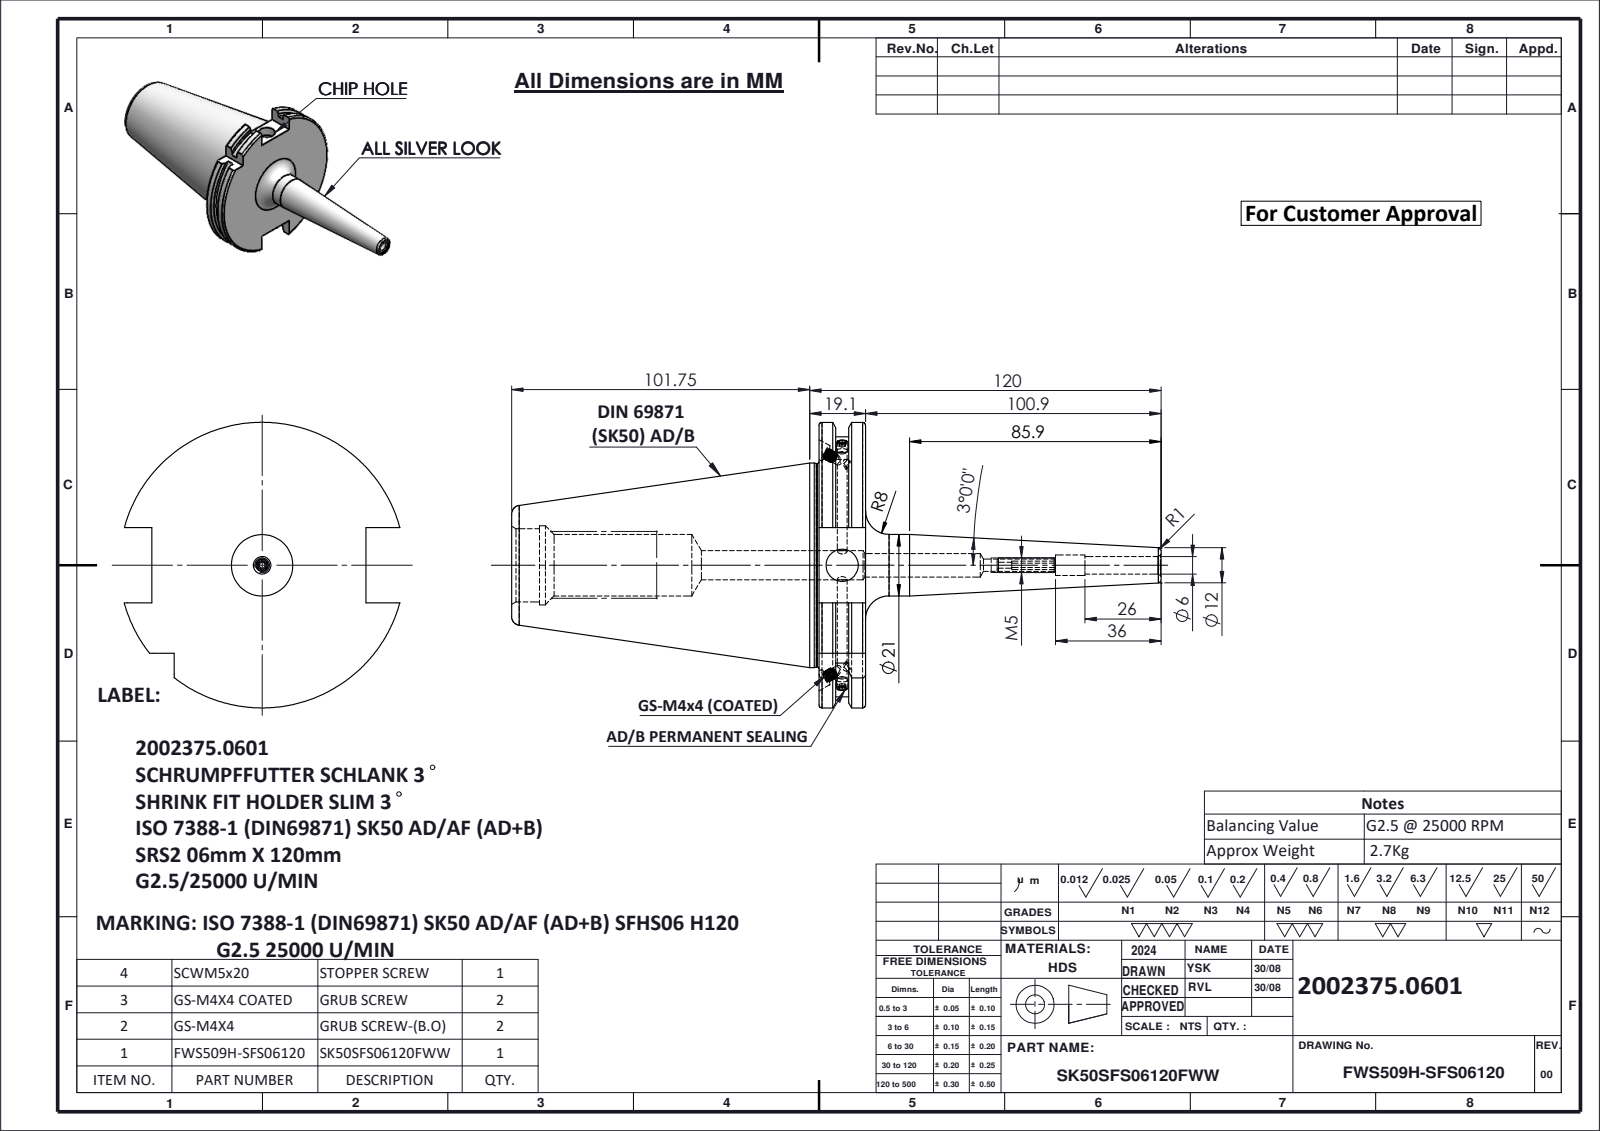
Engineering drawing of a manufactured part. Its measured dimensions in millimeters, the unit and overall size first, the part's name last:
Units: millimetres
Overall size (bounding box): 221.75 × 97.5 × 94.05
Round holes (diameter × count): ⌀6 ×3, ⌀3.2 ×2, ⌀2 ×1, ⌀3.3 ×1, ⌀4.2 ×1, ⌀7 ×1, ⌀8 ×1, ⌀10 ×1, ⌀11 ×1, ⌀21 ×1, ⌀25 ×1, ⌀27 ×1
Round bosses / shafts (diameter × count): ⌀4 ×4, ⌀2.9 ×2, ⌀69.85 ×1, ⌀69.45 ×1, ⌀5 ×1
Partial cylindrical surfaces — rounded edges, fillets, slot ends (radius × count): R44.9 ×1, R48.75 ×1
Main face-to-face distances: 15.9, 5.66, 10.24, 10.14, 4.48, 5.76, 104.95, 110.61, 115.09, 120.85
Volume: 355 411 mm³ · Surface area: 51 305 mm²
Bodies: 6 solids, 285 faces (78 planar, 83 cylindrical, 124 other)
Part name (STEP PRODUCT): SCWM5; GS-M4X4-COATING_DIN 913 - M4 x 4-N; SK50SFS06120FWW; GS-M4X4_DIN 913 - M4 x 4-N (+1 more)
STEP written by: SolidWorks 2024 (CONFIG_CONTROL_DESIGN)
